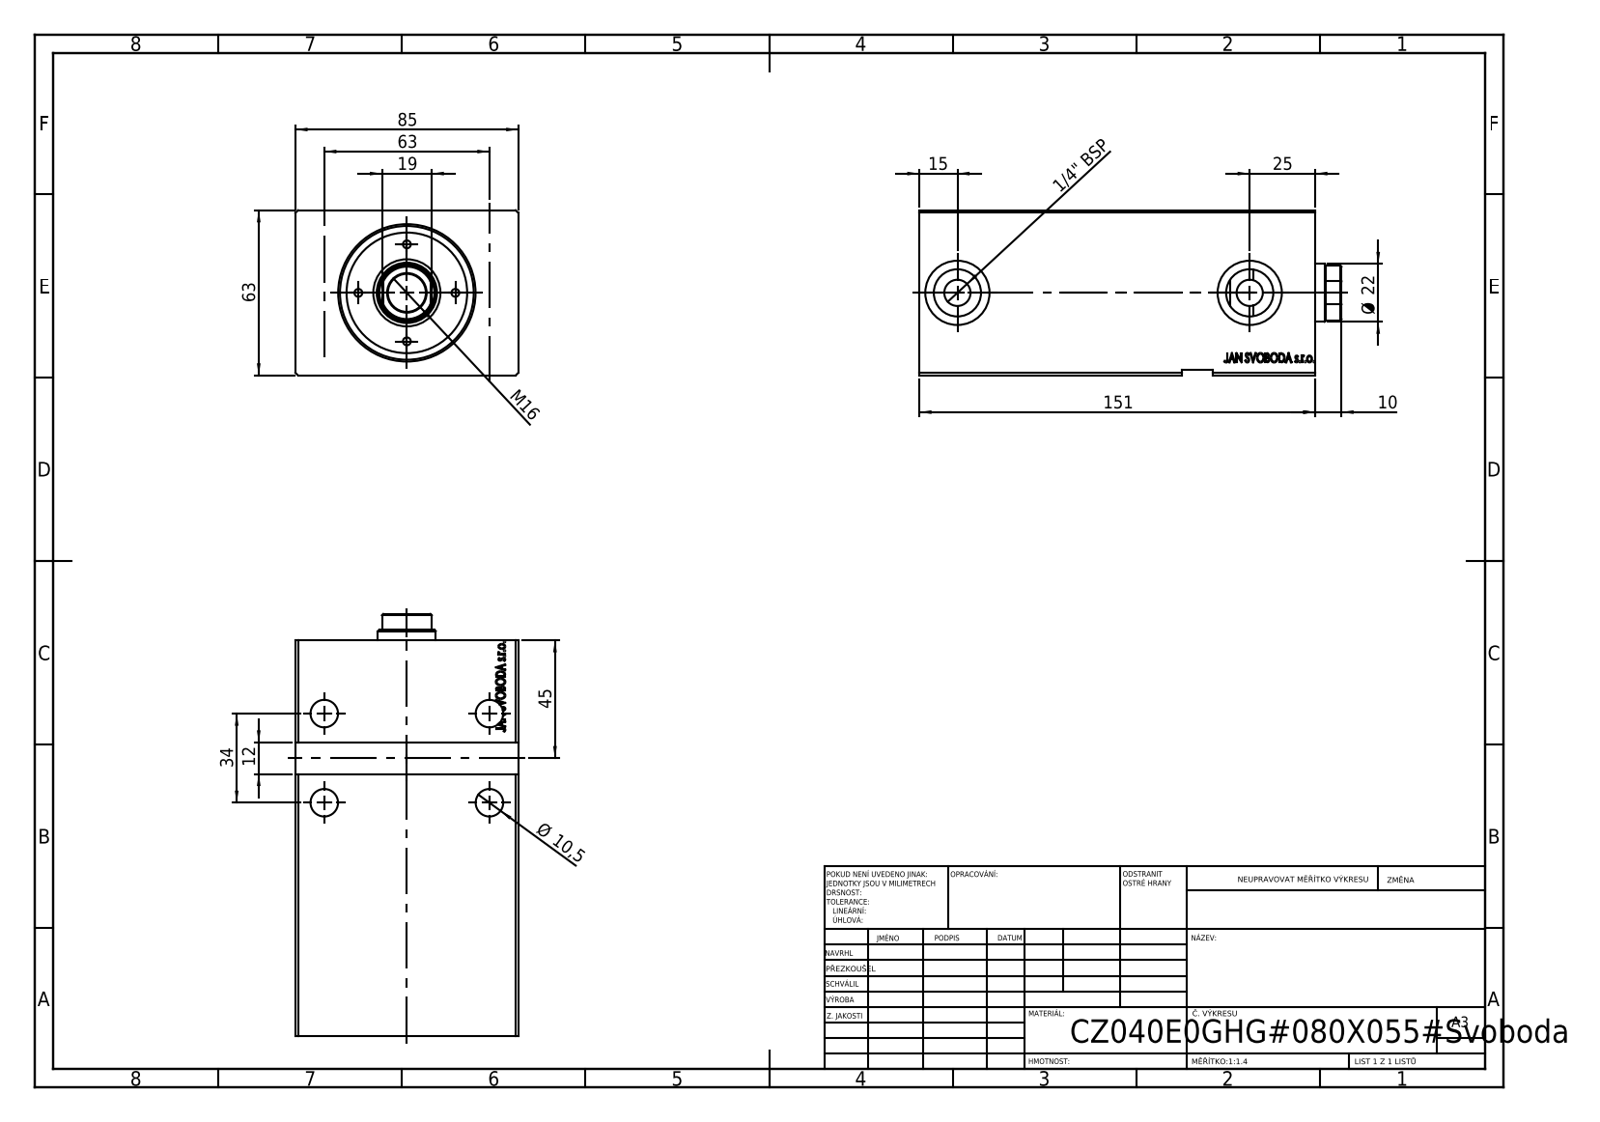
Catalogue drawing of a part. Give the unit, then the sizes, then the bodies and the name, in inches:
Units: inches
Overall size (bounding box): 5.945 × 3.346 × 2.48
Round holes (diameter × count): ⌀0.413 ×4, ⌀0.315 ×2, ⌀0.394 ×2, ⌀0.709 ×2, ⌀0.965 ×2, ⌀1.417 ×1, ⌀1.575 ×1, ⌀2.008 ×1
Main face-to-face distances: 2.48, 3.346, 5.945, 5.343, 0.602, 0.079, 2.402, 5.937, 0.594, 0.394
Hole centre spacings: 1.339, 2.48, 2.819, 0.742, 1.267, 1.813, 2.083, 2.631
Volume: 36.54 in³ · Surface area: 126.9 in²
Bodies: 1 solid, 781 faces (384 planar, 31 cylindrical, 366 other)
STEP written by: SolidWorks 2019 (CONFIG_CONTROL_DESIGN)
